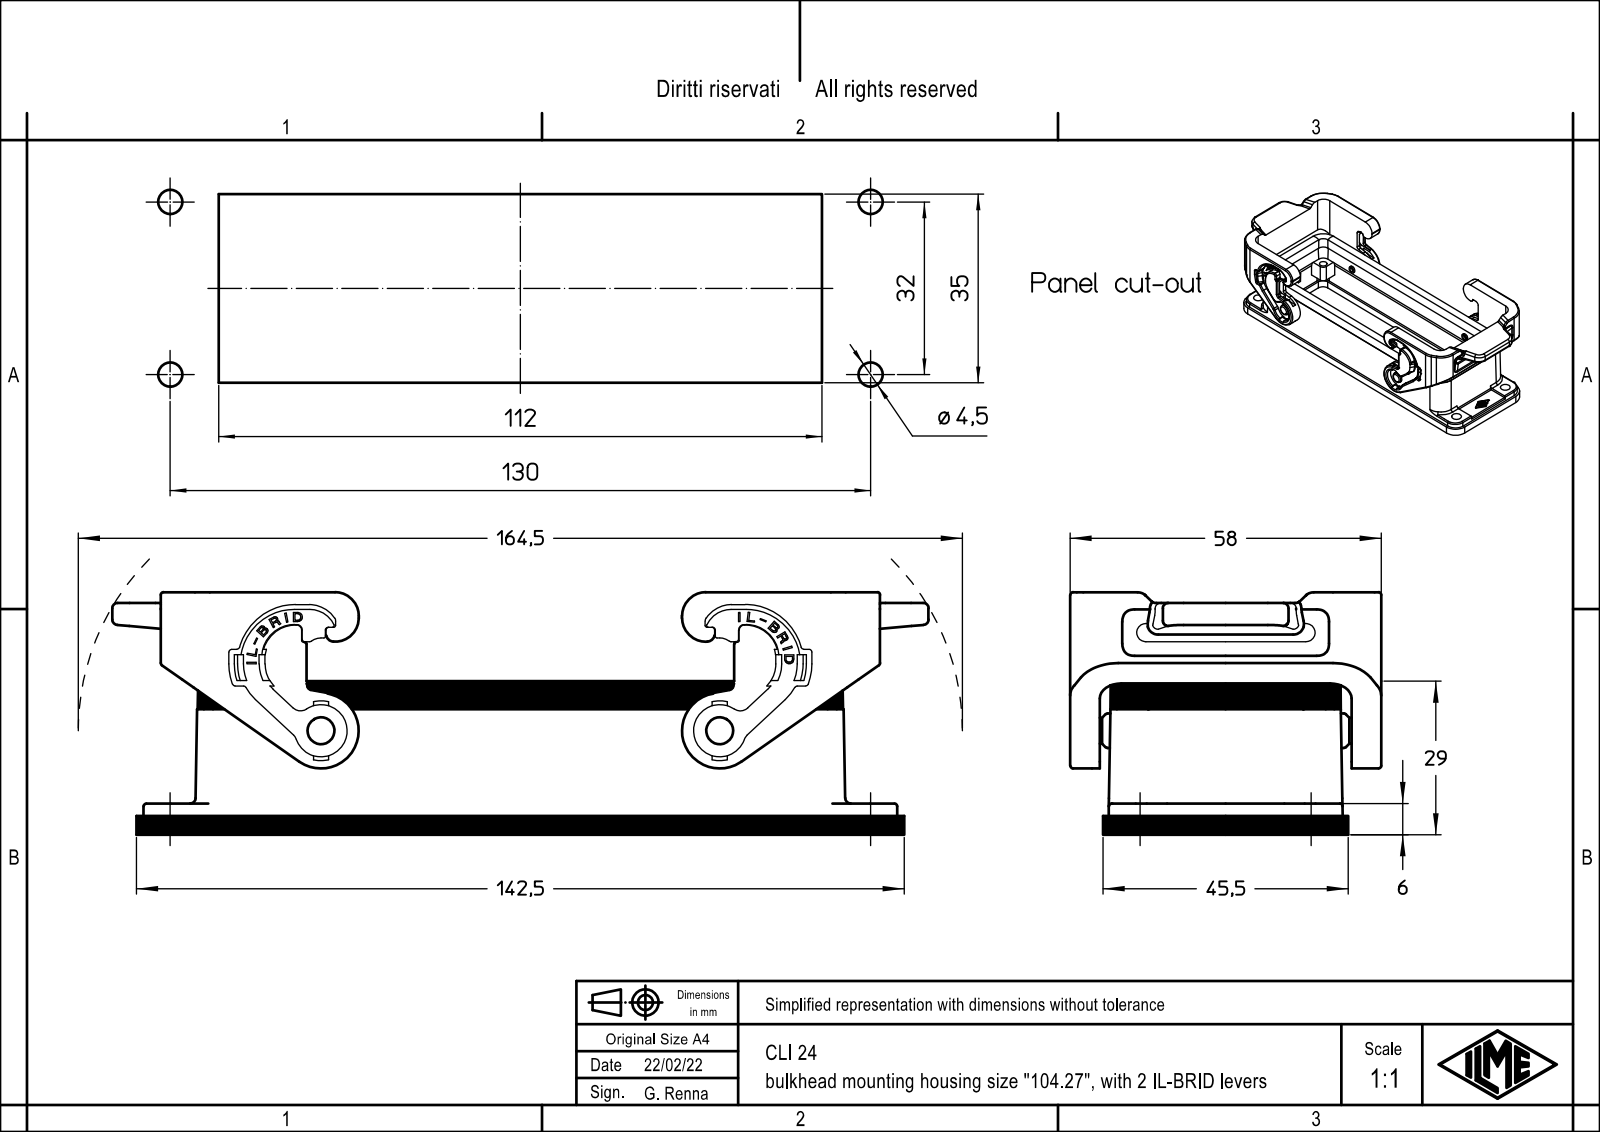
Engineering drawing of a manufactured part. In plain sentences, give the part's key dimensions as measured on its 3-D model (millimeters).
The part is named "CLI_24". Its 3-D file was written by "Creo Elements/Direct Modeling 20.1B 02-Apr-2019 (C) Parametric Technology GmbH (AUTOMOTIVE_DESIGN)". It is 1 solid with 1236 faces: 895 planar, 283 cylindrical and 58 other. Overall it measures 152 by 58 by 45 millimeters. Its volume is 61 147 cubic millimeters and its surface area 38 598 square millimeters. Round holes: 4 of diameter 2.75, 4 of diameter 3.8, 4 of diameter 4.9. Round bosses or shafts: 2 of diameter 6.4, 2 of diameter 4.8. Partial cylindrical surfaces (rounded edges, fillets, slot ends): 32 of radius 1, 16 of radius 3, 15 of radius 0.17, 12 of radius 2, 12 of radius 4, 8 of radius 0.3, 8 of radius 6, 8 of radius 7. The main face-to-face distances are 2, 5, 45, 3.9, 43, 3, 39, 42, 40, 0.75. The hole center spacings are 13.24, 32.24, 117.03, 120.66, 27, 32, 104, 107.45.
